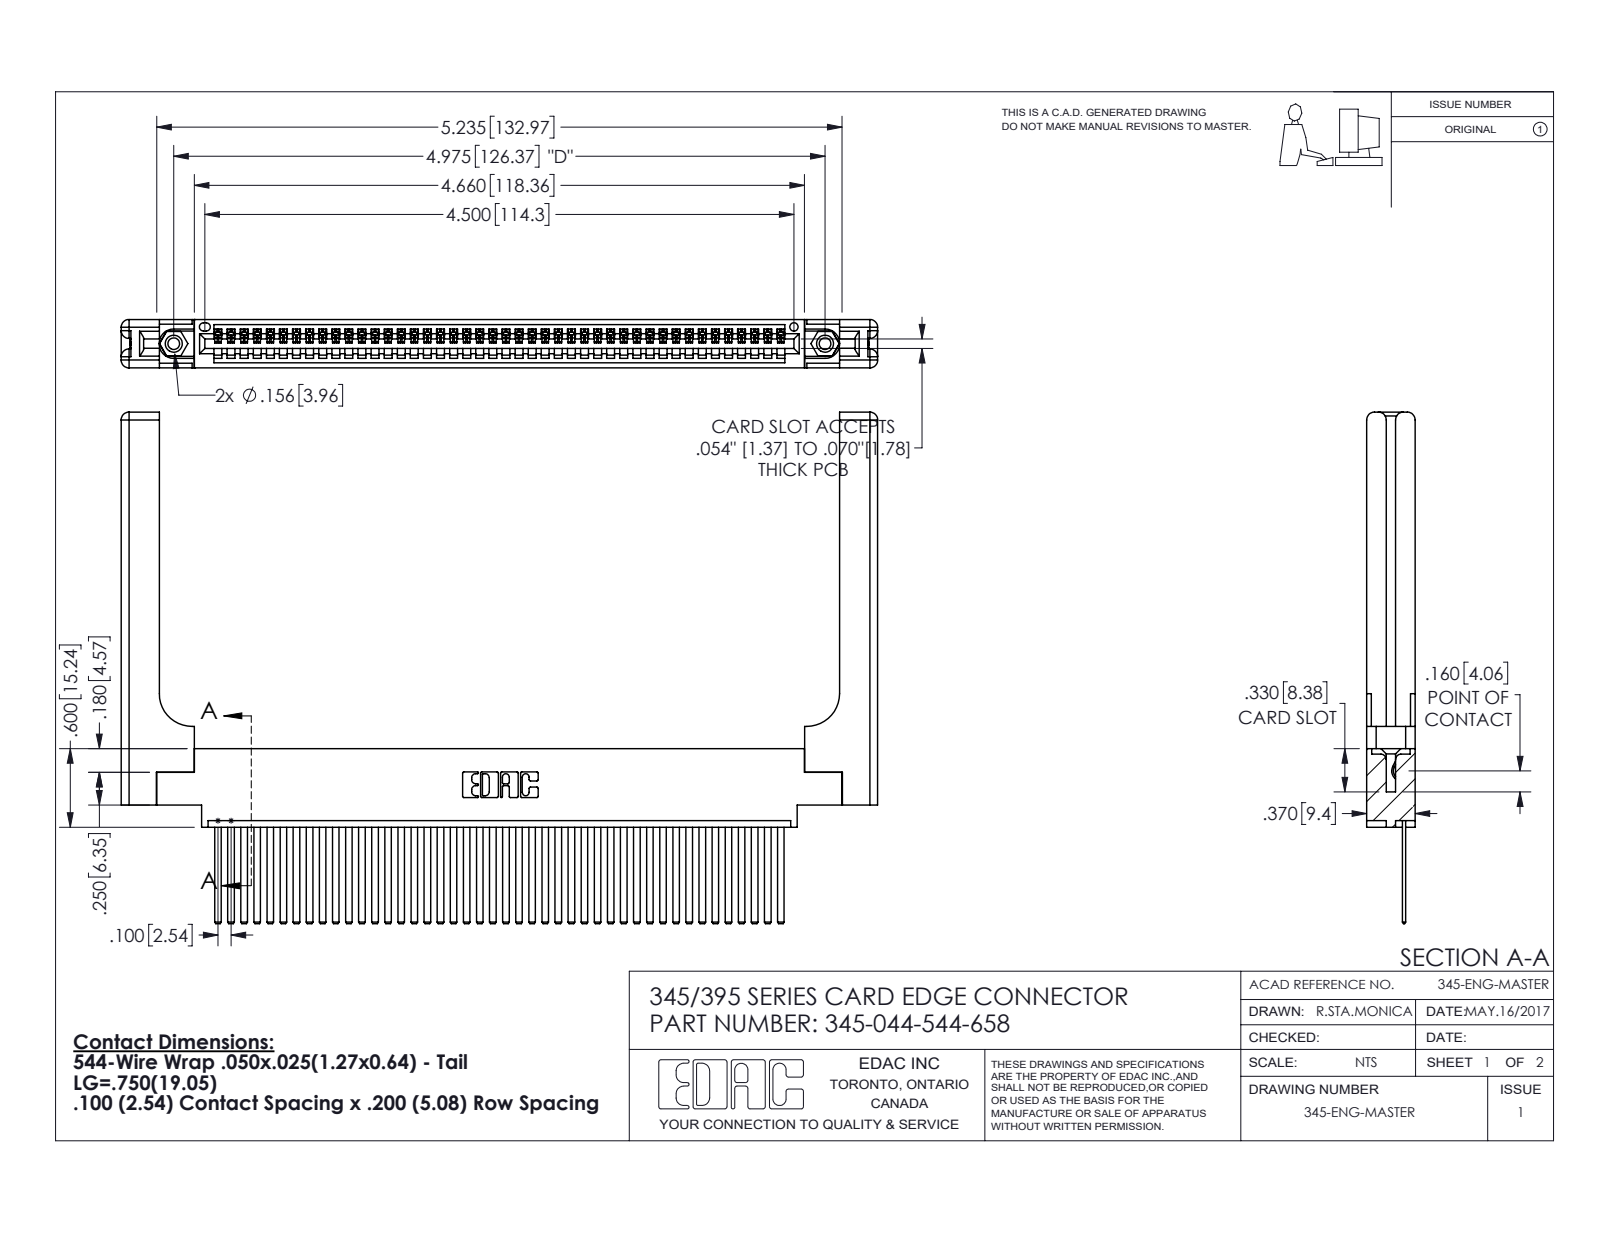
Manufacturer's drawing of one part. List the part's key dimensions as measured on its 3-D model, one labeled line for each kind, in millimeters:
Part name (STEP PRODUCT): 345-044-544-658; 345-220-058_345-220-058; 345-292-001_345-293-144; 345-250-001_345-250-001-102 (+1 more)
STEP written by: SolidWorks 2016 (CONFIG_CONTROL_DESIGN)
Units: millimetres
Bodies: 49 solids, 2674 faces (1816 planar, 798 cylindrical, 60 other)
Overall size (bounding box): 146.8 × 99.2 × 9.4
Volume: 22 860 mm³ · Surface area: 26 060 mm²
Round holes (diameter × count): ⌀2.3 ×2, ⌀3.2 ×2, ⌀4 ×2, ⌀1.6 ×1
Round bosses / shafts (diameter × count): ⌀3.9 ×2
Partial cylindrical surfaces — rounded edges, fillets, slot ends (radius × count): R0.2 ×88, R0.3 ×22, R1.5 ×16, R0.2 ×6, R0.8 ×6, R0.7 ×3, R0.8 ×2, R0.8 ×2
Main face-to-face distances: 1.8, 7.6, 9.4, 2.5, 6.9, 0.6, 5.1, 5.7, 3.8, 3.8
Hole centre spacings: 6.9, 120.4, 126.4
